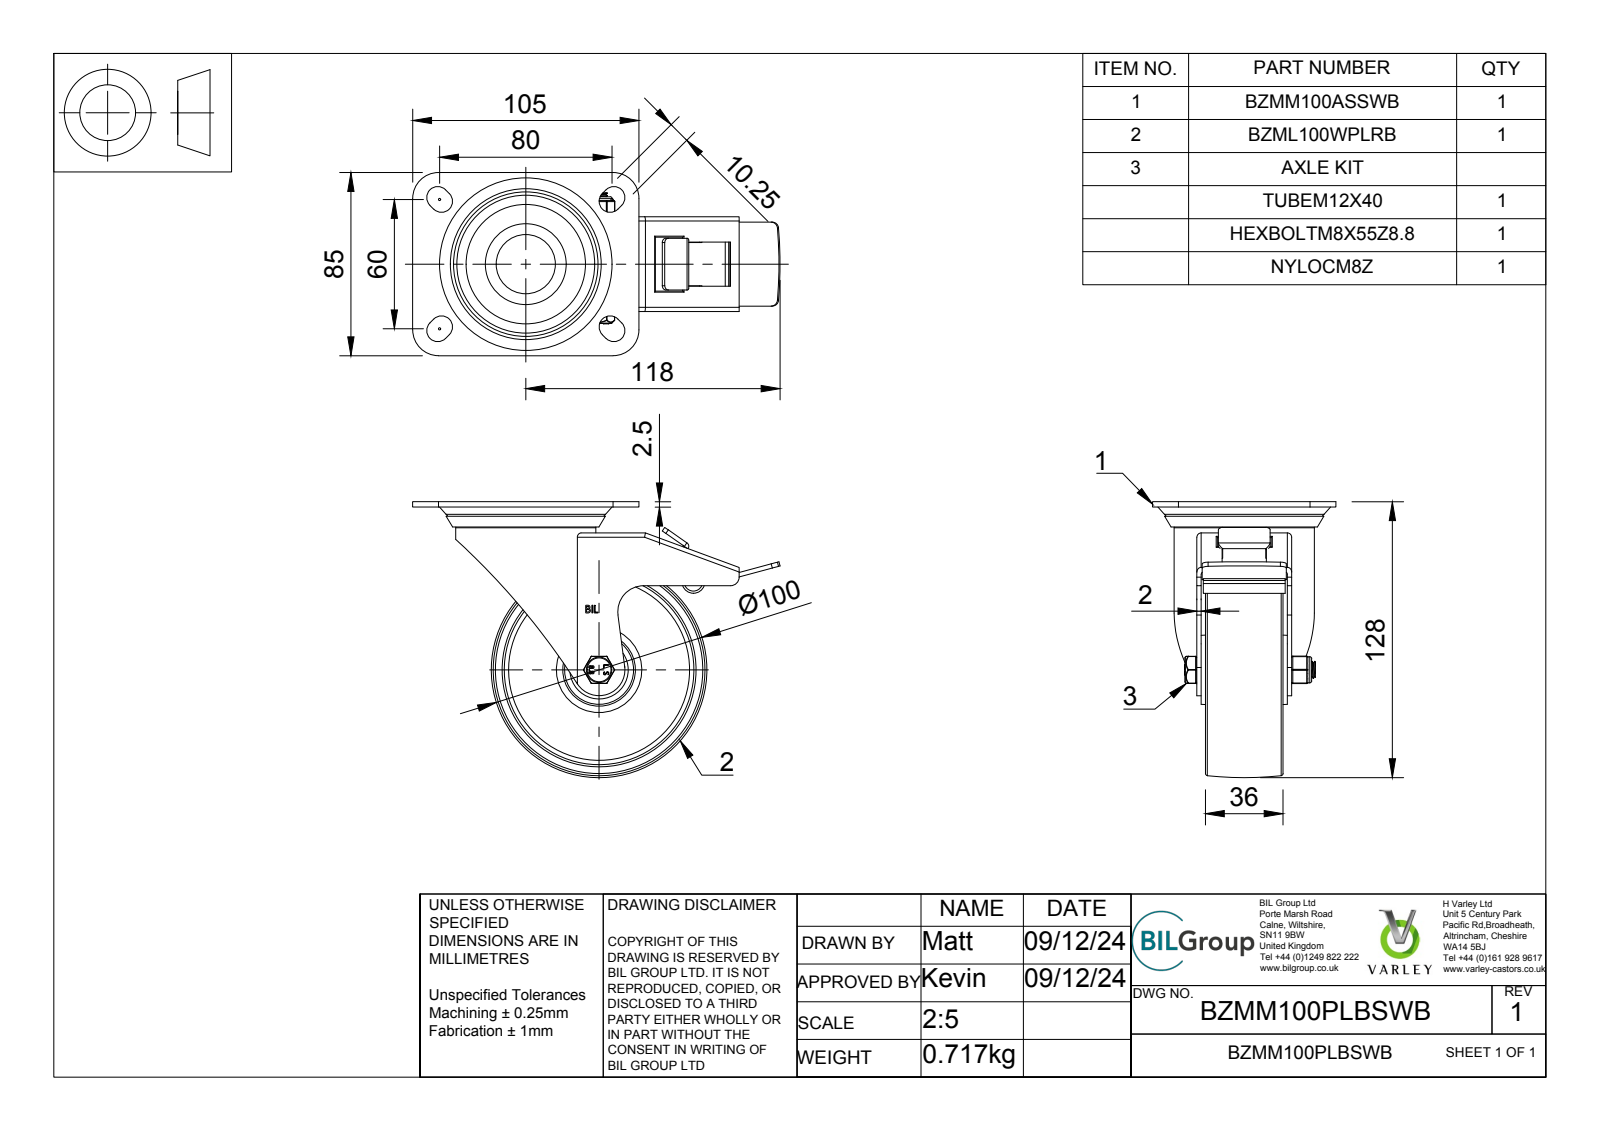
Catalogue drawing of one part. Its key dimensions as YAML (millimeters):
part_name: "BZMM100PLBSWB v3; BZMM100ASSWB v1; ZINC PLATED, PRESSED STEEL TOP PLATE; ZINC PLATED, PRESSED STEEL TOP PLATE Geometry (+7 more)"
step_written_by: "Autodesk Translation Framework v13.20.0.188 (AP242_MANAGED_MODEL_BASED_3D_ENGINEERING_MIM_LF)"
units: millimeters
bodies: {solids: 43, faces: 651, planar: 346, cylindrical: 186, other: 119}
overall_size: [170.5, 128, 85]
volume: 199632
surface_area: 120233
round_holes:
  - {diameter: 0.66, count: 2}
  - {diameter: 8, count: 1}
  - {diameter: 8.2, count: 1}
  - {diameter: 8.4, count: 1}
  - {diameter: 8.6, count: 1}
  - {diameter: 12.5, count: 1}
  - {diameter: 18, count: 1}
  - {diameter: 27, count: 1}
  - {diameter: 27.5, count: 1}
  - {diameter: 56, count: 1}
  - {diameter: 61, count: 1}
  - {diameter: 88, count: 1}
round_bosses_or_shafts:
  - {diameter: 3, count: 8}
  - {diameter: 65, count: 1}
  - {diameter: 31.5, count: 1}
  - {diameter: 12.1, count: 1}
  - {diameter: 11.9, count: 1}
  - {diameter: 11.5, count: 1}
  - {diameter: 7.87, count: 1}
  - {diameter: 6.45, count: 1}
partial_cylinders:
  - {radius: 0.5, count: 22}
  - {radius: 0.25, count: 12}
  - {radius: 2, count: 9}
  - {radius: 5.12, count: 8}
  - {radius: 1, count: 6}
  - {radius: 12, count: 5}
  - {radius: 0.33, count: 4}
  - {radius: 0.64, count: 4}
face_to_face_distances: [2, 16.5, 23.5, 18.5, 25.5, 40, 42, 7, 2.5, 14.5]
hole_center_spacings: [3.22, 2.49]
